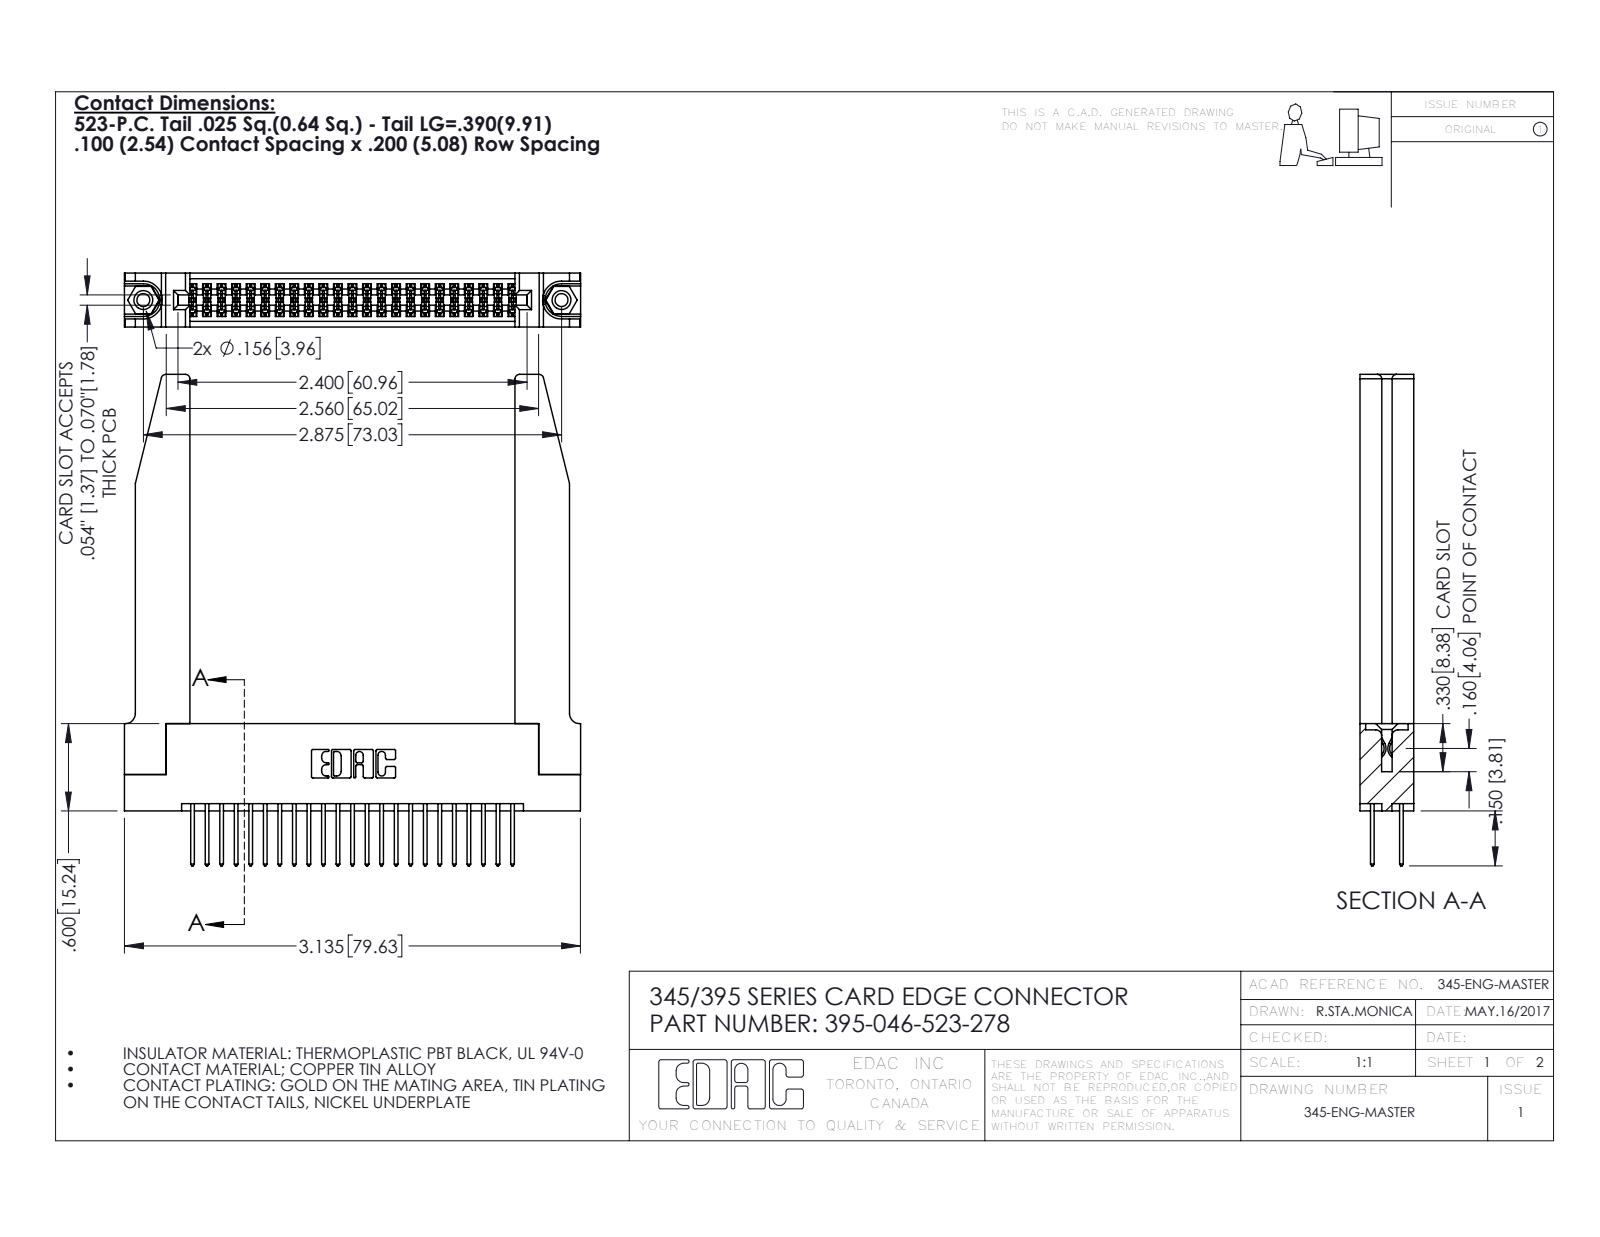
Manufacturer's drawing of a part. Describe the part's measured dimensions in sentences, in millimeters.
The part is named "345-220-078_345-220-078; 345-250-001_345-250-001-102; 345-292-001_345-293-123; 395-046-523-278 (+1 more)". Its 3-D file was written by "SolidWorks 2016 (CONFIG_CONTROL_DESIGN)". It is 51 solids with 2660 faces: 1740 planar, 868 cylindrical and 52 other. Overall it measures 85.8 by 79.7 by 9.4 millimeters. Its volume is 15 400 cubic millimeters and its surface area 18 210 square millimeters. Round holes: 2 of diameter 2.3, 2 of diameter 3.2, 2 of diameter 4, 1 of diameter 1.6. Round bosses or shafts: 2 of diameter 3.9. Partial cylindrical surfaces (rounded edges, fillets, slot ends): 69 of radius 0.2, 46 of radius 0.3, 22 of radius 0.3, 8 of radius 0.8, 6 of radius 0.2, 6 of radius 0.8, 3 of radius 0.7, 2 of radius 0.4. The main face-to-face distances are 9.4, 1.8, 7.6, 5.1, 2.5, 6.9, 0.6, 5.7, 3.8, 3.8. The hole center spacings are 6.9, 67.1, 73.
